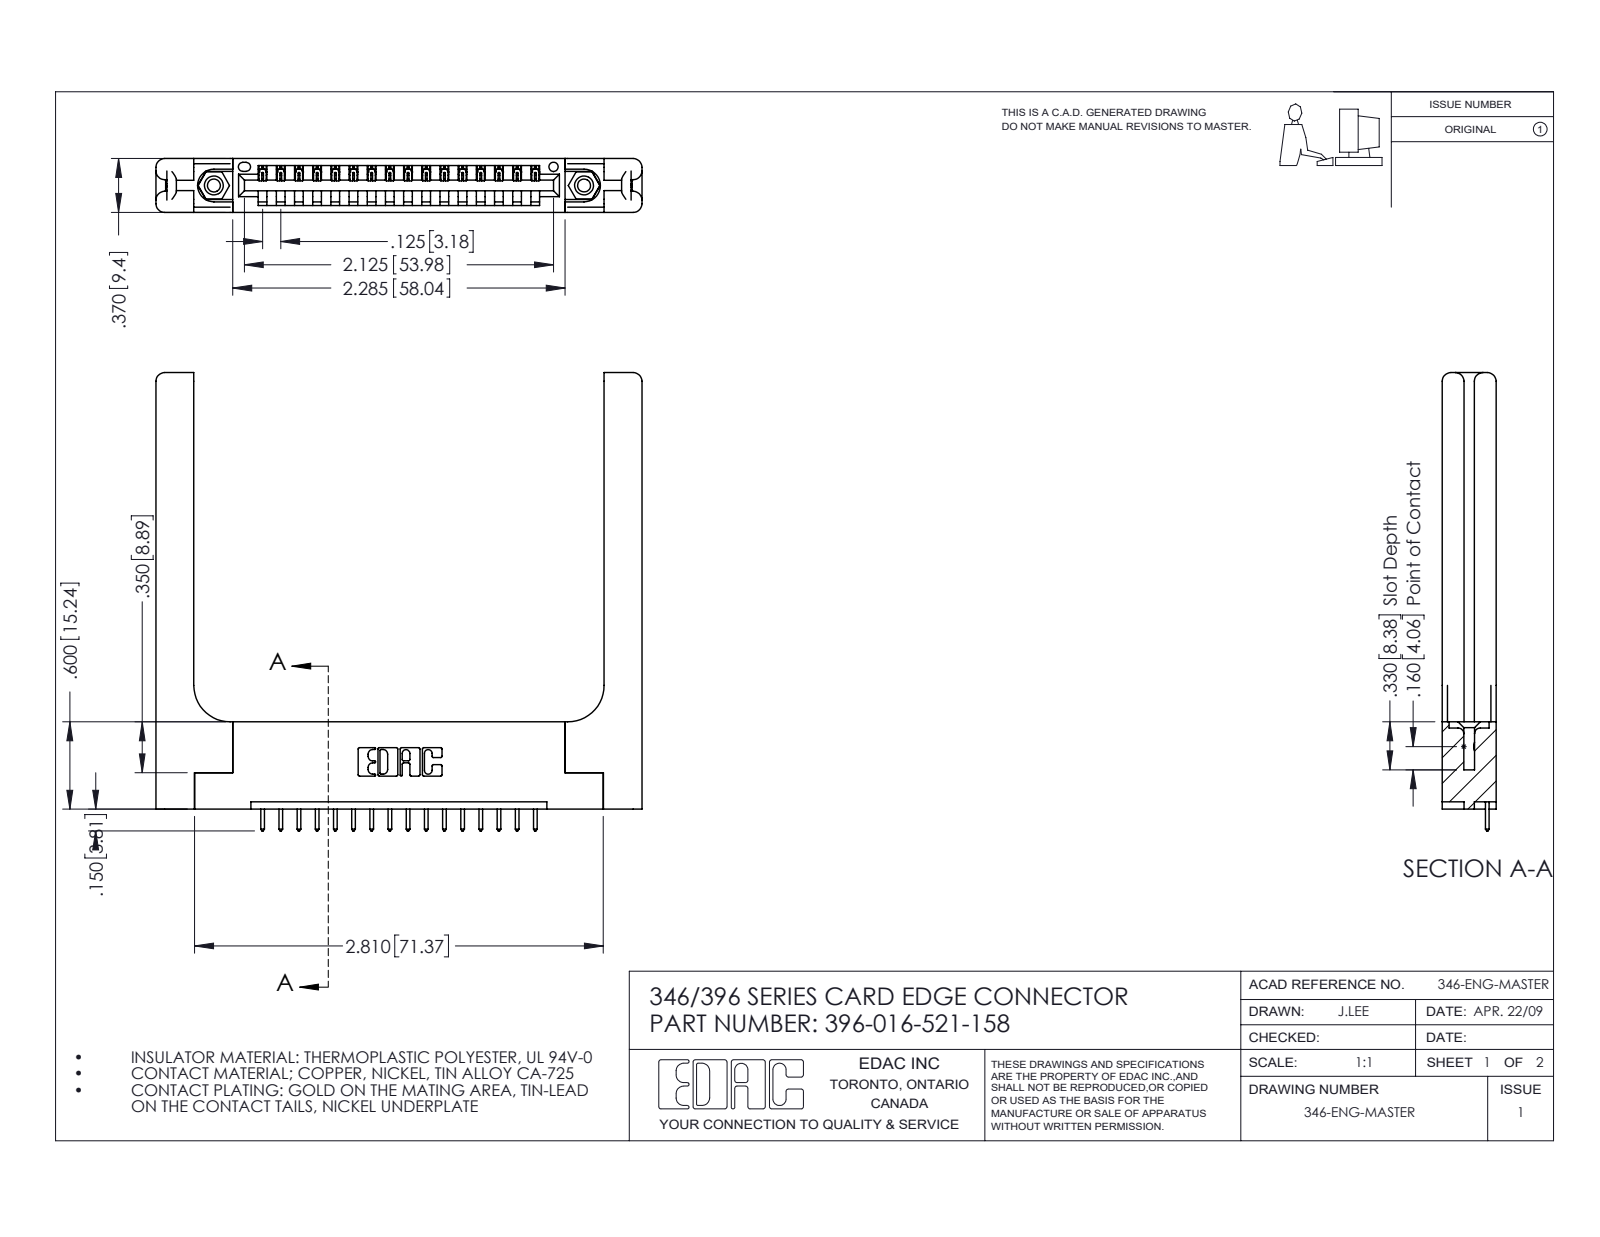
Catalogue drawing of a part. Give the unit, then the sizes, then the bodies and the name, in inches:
Units: inches
Overall size (bounding box): 3.341 × 3.15 × 0.37
Round holes (diameter × count): ⌀0.089 ×2, ⌀0.125 ×2, ⌀0.156 ×2, ⌀0.064 ×1
Round bosses / shafts (diameter × count): ⌀0.155 ×2
Partial cylindrical surfaces — rounded edges, fillets, slot ends (radius × count): R0.006 ×32, R0.01 ×32, R0.01 ×22, R0.06 ×16, R0.007 ×6, R0.031 ×6, R0.026 ×3, R0.03 ×2
Main face-to-face distances: 0.37, 0.15, 0.072, 0.148, 0.048, 0.322, 0.25, 0.102, 0.22, 0.173
Hole centre spacings: 0.246, 2.338, 2.545
Volume: 0.941 in³ · Surface area: 22.6 in²
Bodies: 21 solids, 1306 faces (864 planar, 382 cylindrical, 60 other)
Part name (STEP PRODUCT): 346-220-058_345-220-058; 396-016-521-158; 345-292-001_345-293-121; 345-250-001_345-250-001-102 (+1 more)
STEP written by: SolidWorks 2016 (CONFIG_CONTROL_DESIGN)
